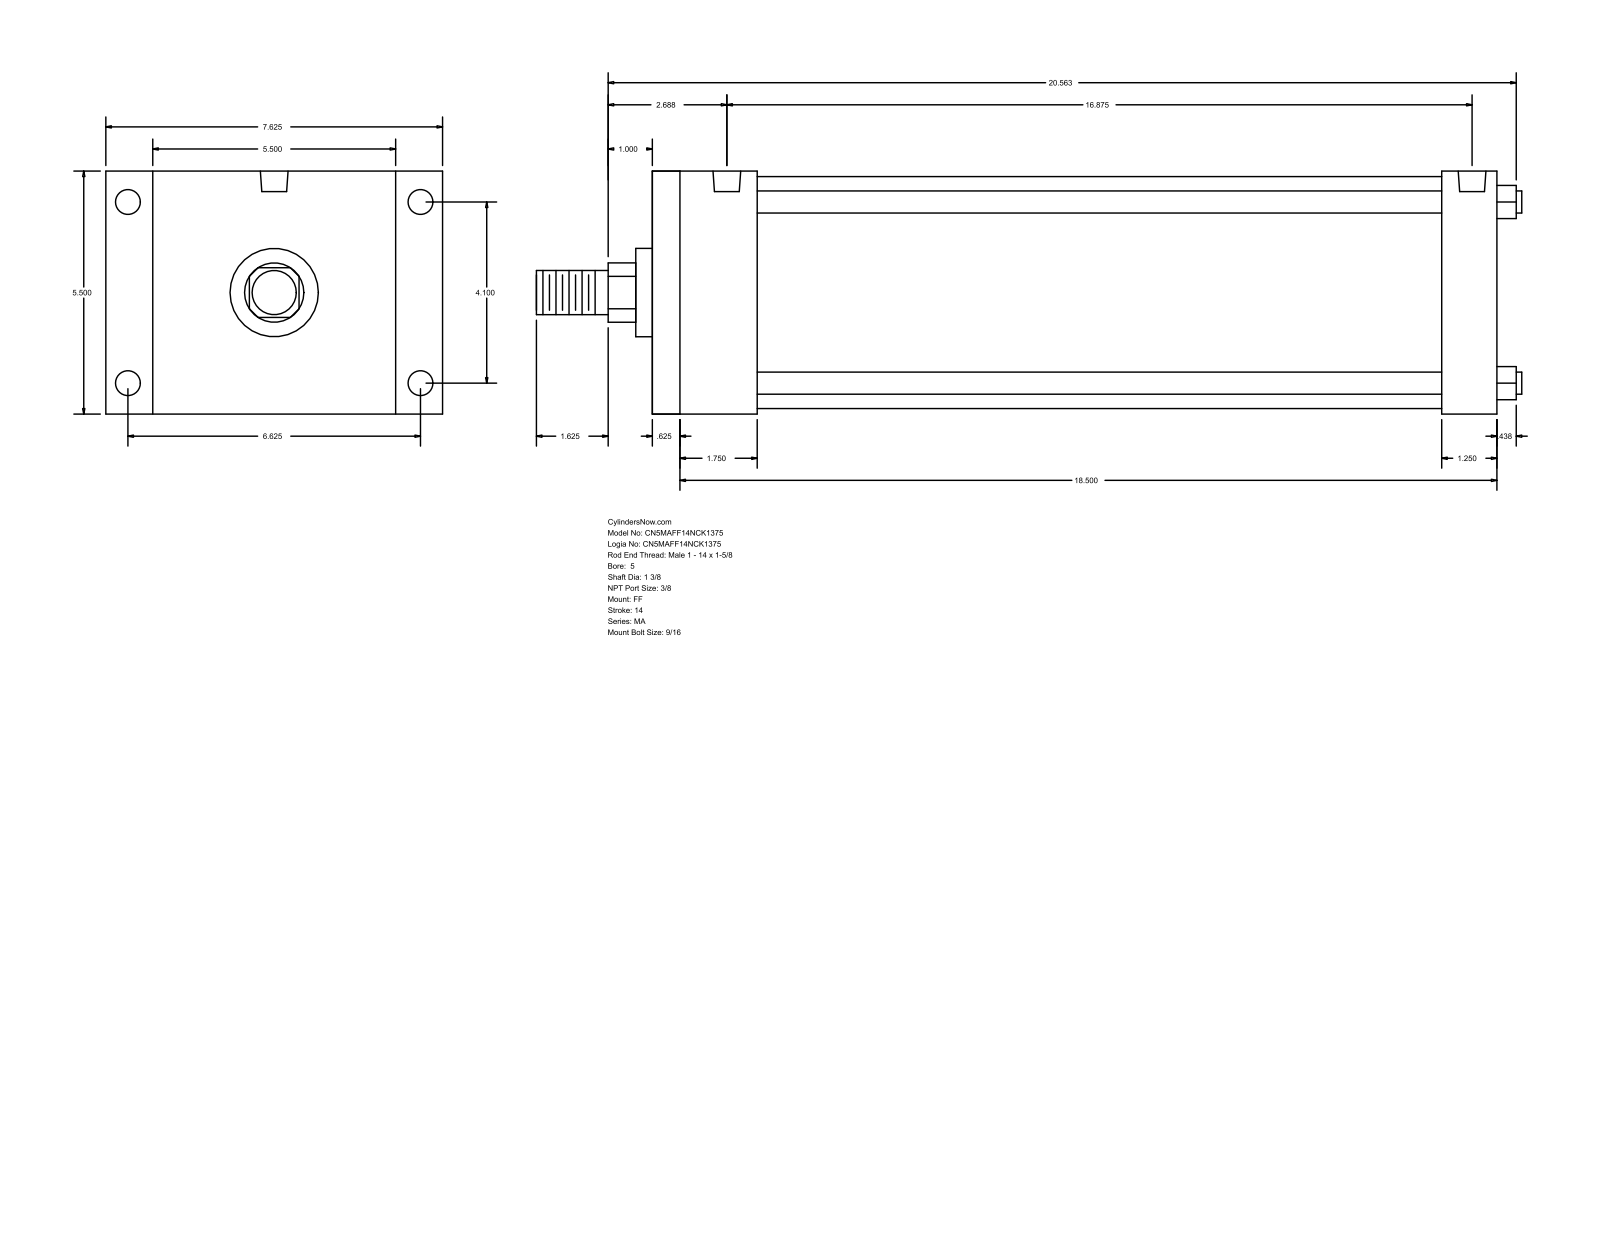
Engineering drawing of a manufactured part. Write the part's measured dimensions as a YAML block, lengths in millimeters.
part_name: "MA_FF__0500_1.375"
step_written_by: "GSSL Pune (CONFIG_CONTROL_DESIGN)"
units: millimeters
bodies: {solids: 0, faces: 92, planar: 64, cylindrical: 28, other: 0}
overall_size: [566.74, 193.68, 139.7]
round_holes:
  - {diameter: 11.11, count: 4}
  - {diameter: 14.29, count: 4}
  - {diameter: 15.93, count: 2}
round_bosses_or_shafts:
  - {diameter: 12.7, count: 4}
  - {diameter: 133.35, count: 1}
  - {diameter: 50.8, count: 1}
  - {diameter: 34.92, count: 1}
  - {diameter: 25.4, count: 1}
partial_cylinders:
  - {radius: 17.06, count: 1}
face_to_face_distances: [139.7, 485.78, 15.87, 469.91, 454.03, 438.16, 31.75, 60.32, 44.45, 393.71]
hole_center_spacings: [4.77, 104.14, 168.28, 197.9, 419.09, 423.86, 428.63]
